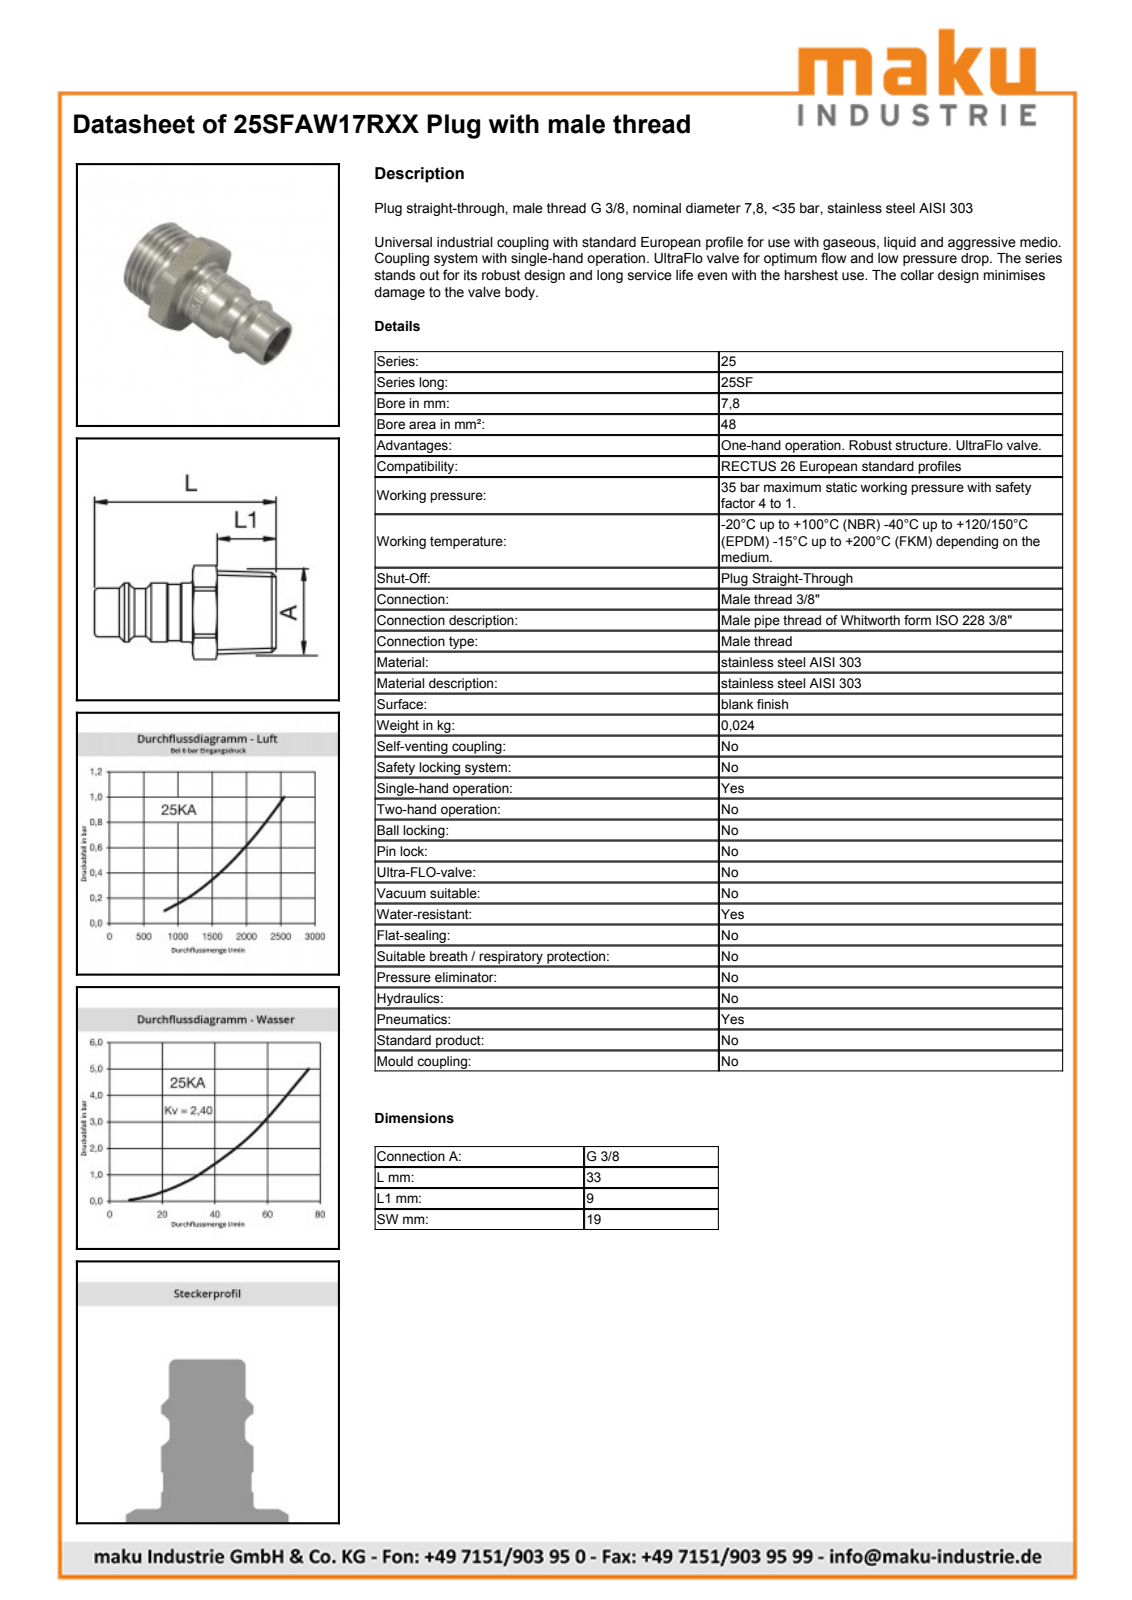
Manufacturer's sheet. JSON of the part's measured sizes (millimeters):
{"part_name": "D103663", "step_written_by": "Autodesk Inventor 2011 (AUTOMOTIVE_DESIGN)", "units": "millimeters", "bodies": {"solids": 1, "faces": 44, "planar": 10, "cylindrical": 12, "other": 22}, "overall_size": [33.1, 21.4, 19], "volume_mm3": 3189, "surface_area_mm2": 2726, "round_holes": [[7.85, 1]], "round_bosses_or_shafts": [[16.6, 1], [12, 1], [9.9, 1], [9.75, 1]], "partial_cylinders_radius": [[10.7, 1]], "face_to_face_distances": [19, 4.1, 13.1, 9, 20, 24.1, 33.1]}
